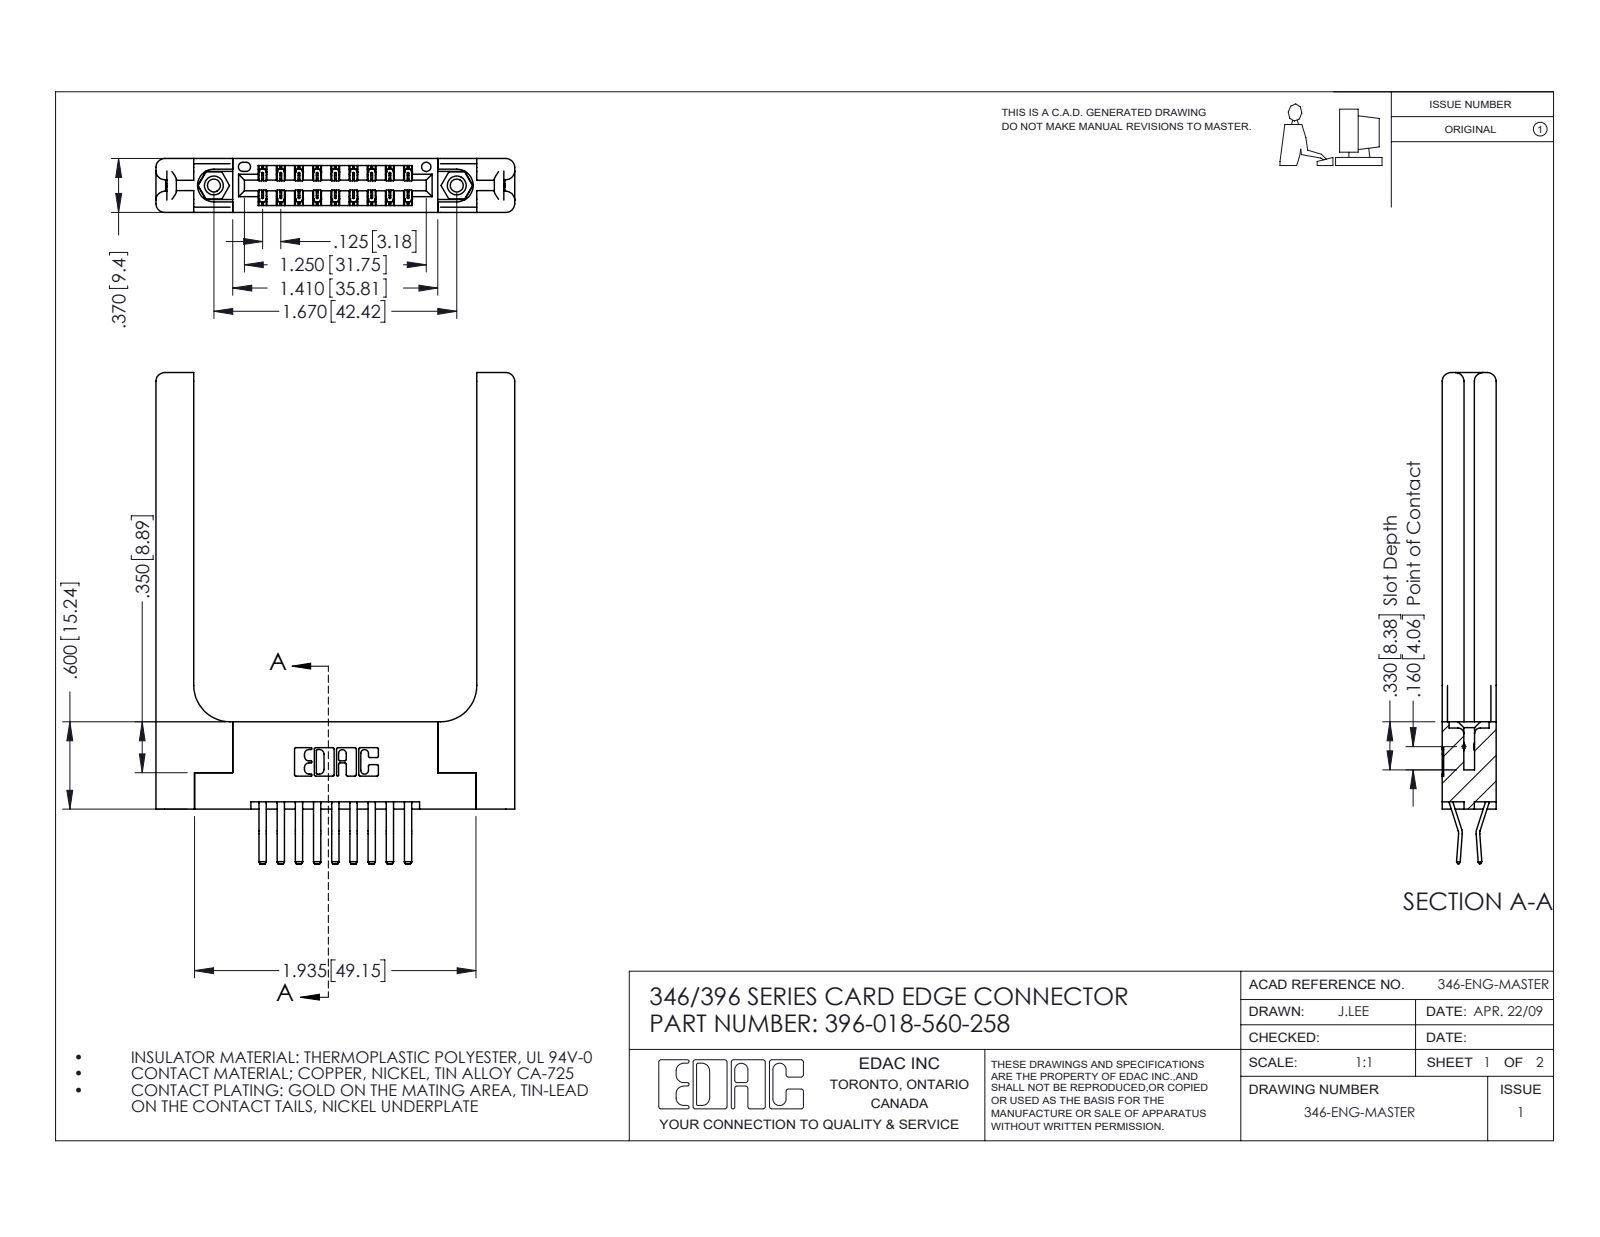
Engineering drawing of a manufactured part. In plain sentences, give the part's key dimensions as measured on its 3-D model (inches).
The part is named "346 Part_Flush Mounting Lugs - 0.156 Dia-TH; 345-292-001_560 Tail; 346-220-058_345-220-058; 396-018-560-258 (+1 more)". Its 3-D file was written by "SolidWorks 2016 (CONFIG_CONTROL_DESIGN)". It is 23 solids with 1350 faces: 854 planar, 436 cylindrical and 60 other. Overall it measures 3.375 by 2.466 by 0.37 inches. Its volume is 0.822 cubic inches and its surface area 20.11 square inches. Round holes: 2 of diameter 0.089, 2 of diameter 0.125, 2 of diameter 0.156, 1 of diameter 0.064. Round bosses or shafts: 2 of diameter 0.155. Partial cylindrical surfaces (rounded edges, fillets, slot ends): 27 of radius 0.006, 22 of radius 0.01, 16 of radius 0.06, 6 of radius 0.007, 6 of radius 0.031, 3 of radius 0.026, 2 of radius 0.01, 2 of radius 0.014. The main face-to-face distances are 0.37, 0.15, 0.22, 0.072, 0.148, 0.25, 0.102, 0.048, 0.322, 0.173. The hole center spacings are 0.246, 1.465, 1.67.
